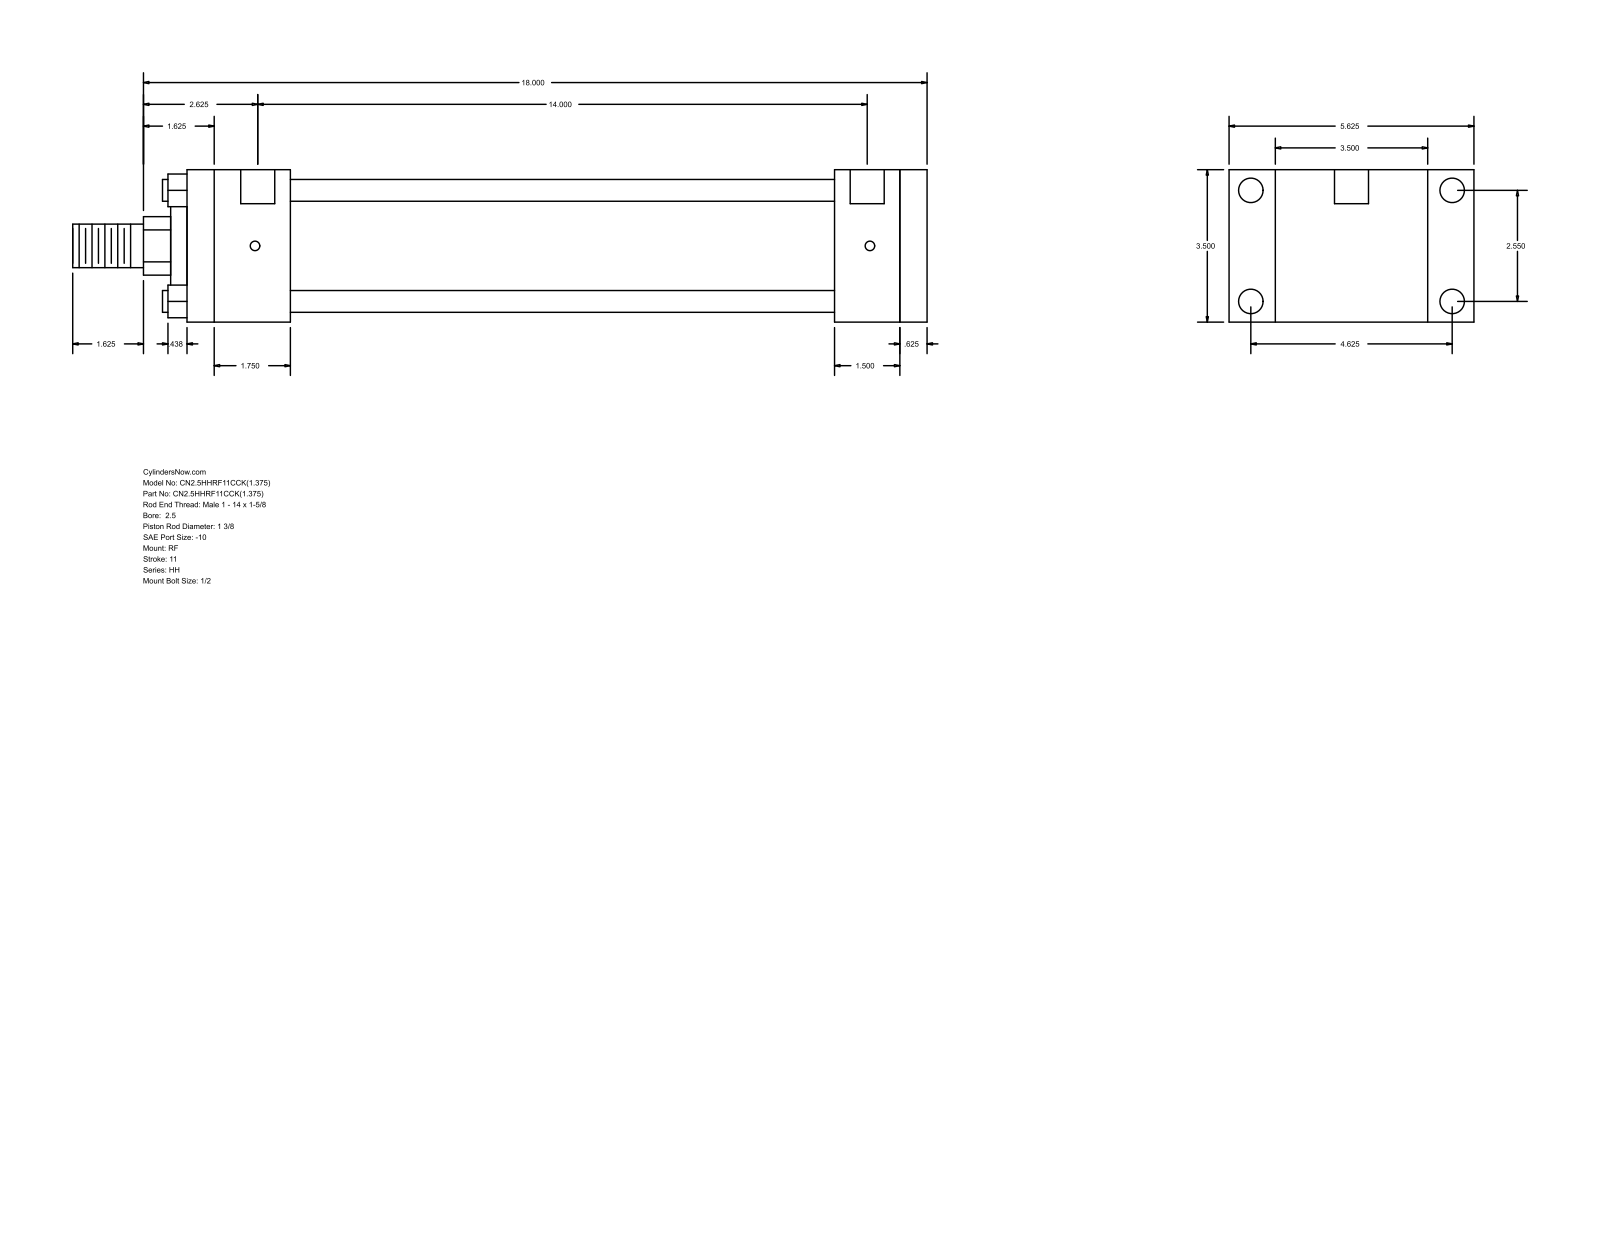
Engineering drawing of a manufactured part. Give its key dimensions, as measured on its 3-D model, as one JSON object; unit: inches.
{"part_name": "HH_RF__0250_1.375", "step_written_by": "GSSL Pune (CONFIG_CONTROL_DESIGN)", "units": "inches", "bodies": {"solids": 0, "faces": 92, "planar": 64, "cylindrical": 28, "other": 0}, "overall_size": [19.625, 5.625, 3.5], "round_holes": [[0.219, 4], [0.563, 4], [0.781, 2]], "round_bosses_or_shafts": [[0.5, 4], [2.875, 1], [2, 1], [1.375, 1], [1, 1]], "partial_cylinders_radius": [[0.672, 1]], "face_to_face_distances": [3.5, 17, 0.625, 16.375, 2.125, 2.375, 14, 14.625, 14.875, 12.5], "hole_center_spacings": [2.55, 4.625, 5.281, 14.125, 0.062, 0.063, 14, 14.062]}
